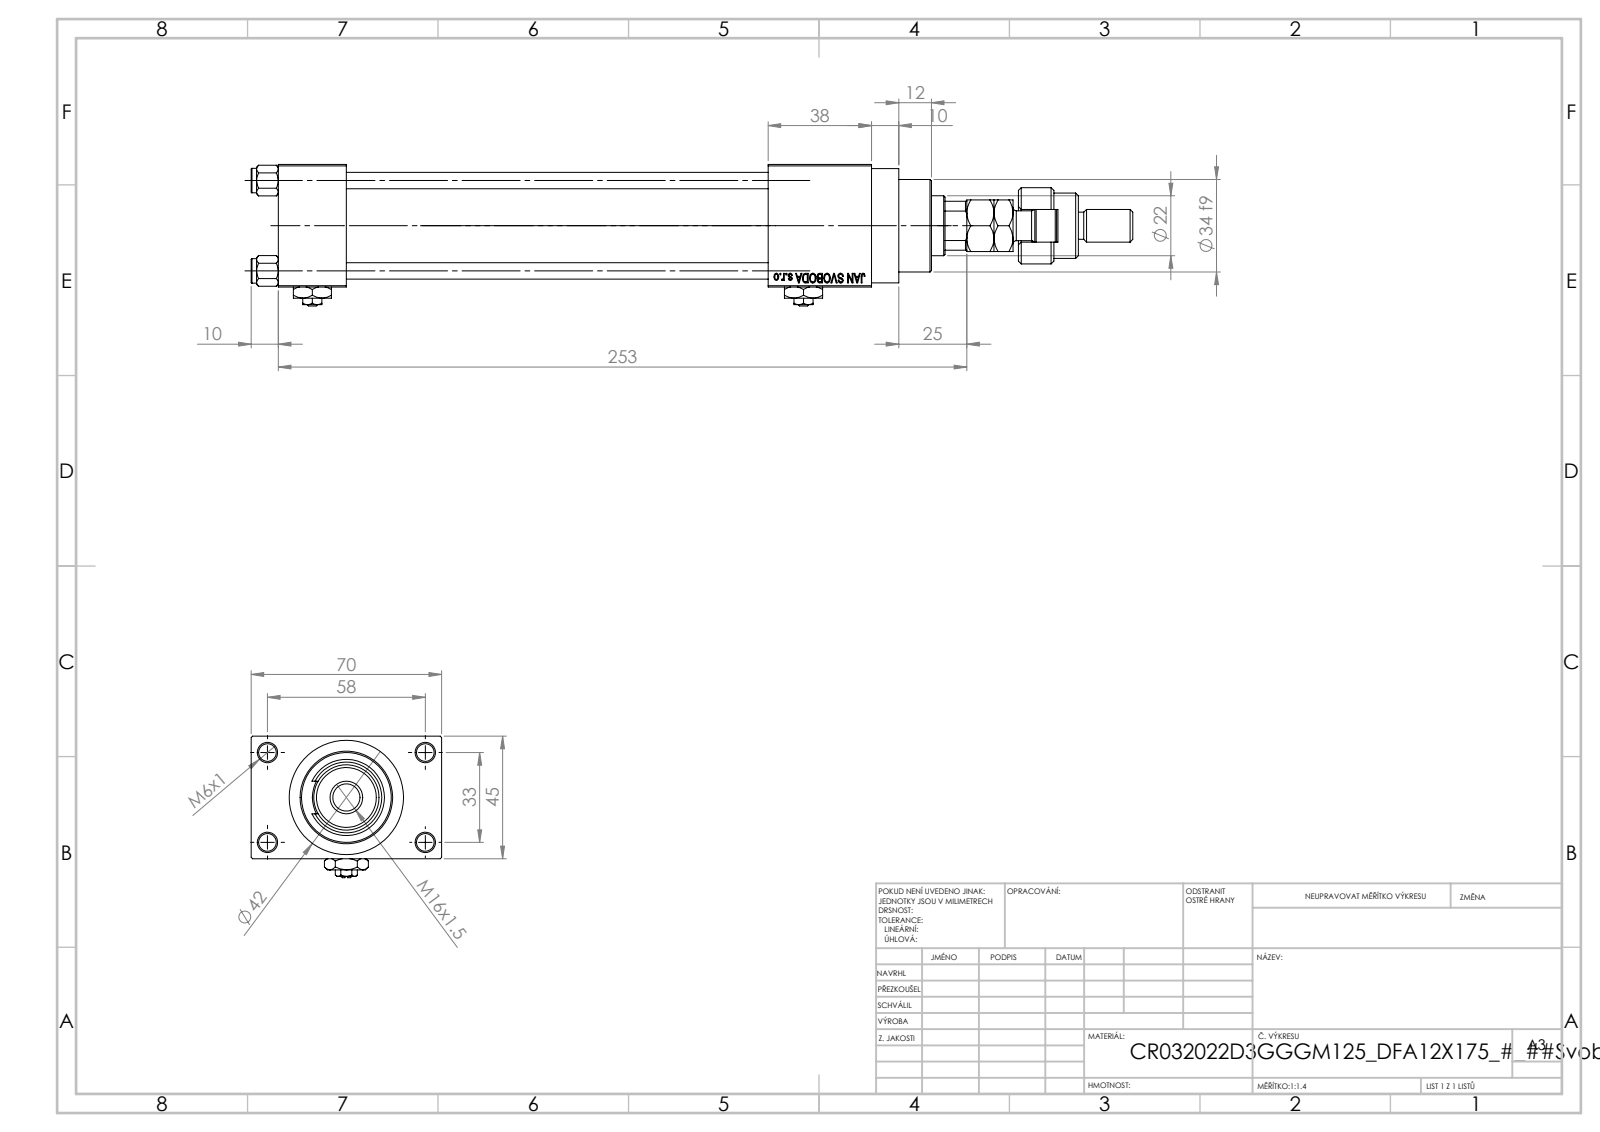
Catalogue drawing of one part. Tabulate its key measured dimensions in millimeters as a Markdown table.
| quantity | value |
| --- | --- |
| part name | NUT_M5_D; V215CR_D_Body; V215CR_VCP_D; V215_VC_A (+4 more) |
| STEP written by | SolidWorks 2019 (CONFIG_CONTROL_DESIGN) |
| units | millimeters |
| bodies | 15 solids, 1287 faces (570 planar, 113 cylindrical, 604 other) |
| overall size | 324 × 70 × 52 |
| volume | 347 673 mm³ |
| surface area | 126 586 mm² |
| round holes (diameter × count) | 6 × 4, 6.5 × 4, 7 × 2, 13.16 × 2, 20 × 2, 10.5 × 1, 22 × 1, 24 × 1, 25 × 1, 32 × 1, 33 × 1 |
| round bosses / shafts (diameter × count) | 9 × 4, 42 × 1, 38 × 1, 34 × 1, 28 × 1, 18 × 1, 12 × 1, 11 × 1 |
| partial cylindrical surfaces (radius × count) | 9.75 × 1, 10.5 × 1 |
| main face-to-face distances | 45, 25, 12.5, 57.5, 155, 180, 38, 193, 70, 218 |
| hole center spacings | 12.4, 23.48, 33.2, 33.37, 35.35, 45.6, 56.35, 33 |
